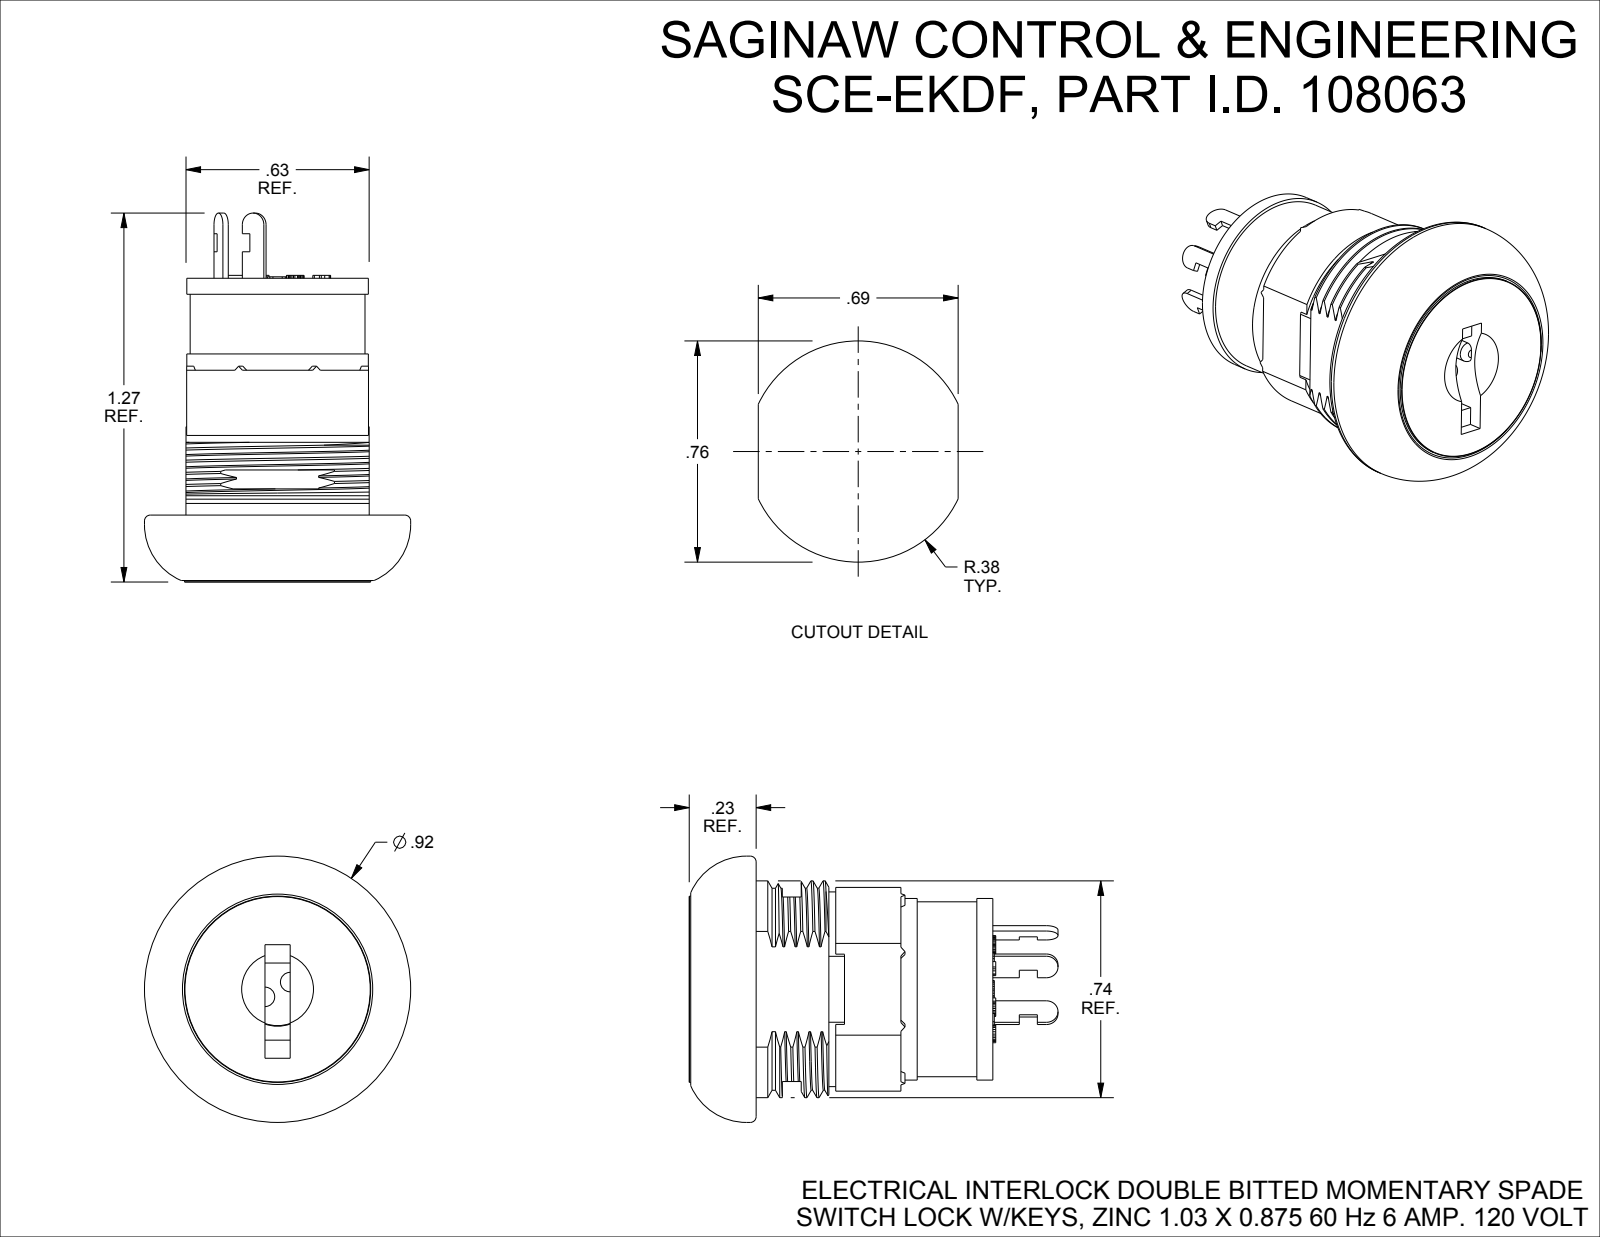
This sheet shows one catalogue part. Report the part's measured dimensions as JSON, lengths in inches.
{"part_name": "SCE-EKDF", "step_written_by": "SolidWorks 2019 (AUTOMOTIVE_DESIGN)", "units": "inches", "bodies": {"solids": 2, "faces": 57, "planar": 36, "cylindrical": 16, "other": 5}, "overall_size": [1.268, 0.915, 0.915], "volume_in3": 0.423, "surface_area_in2": 4.553, "round_bosses_or_shafts": [[0.915, 1], [0.624, 1], [0.601, 1]], "partial_cylinders_radius": [[0.04, 5], [0.334, 1], [0.35, 1], [0.372, 1]], "face_to_face_distances": [0.814, 1.044, 0.23, 0.63, 0.627, 0.628, 0.625, 0.316, 0.498, 0.728]}
